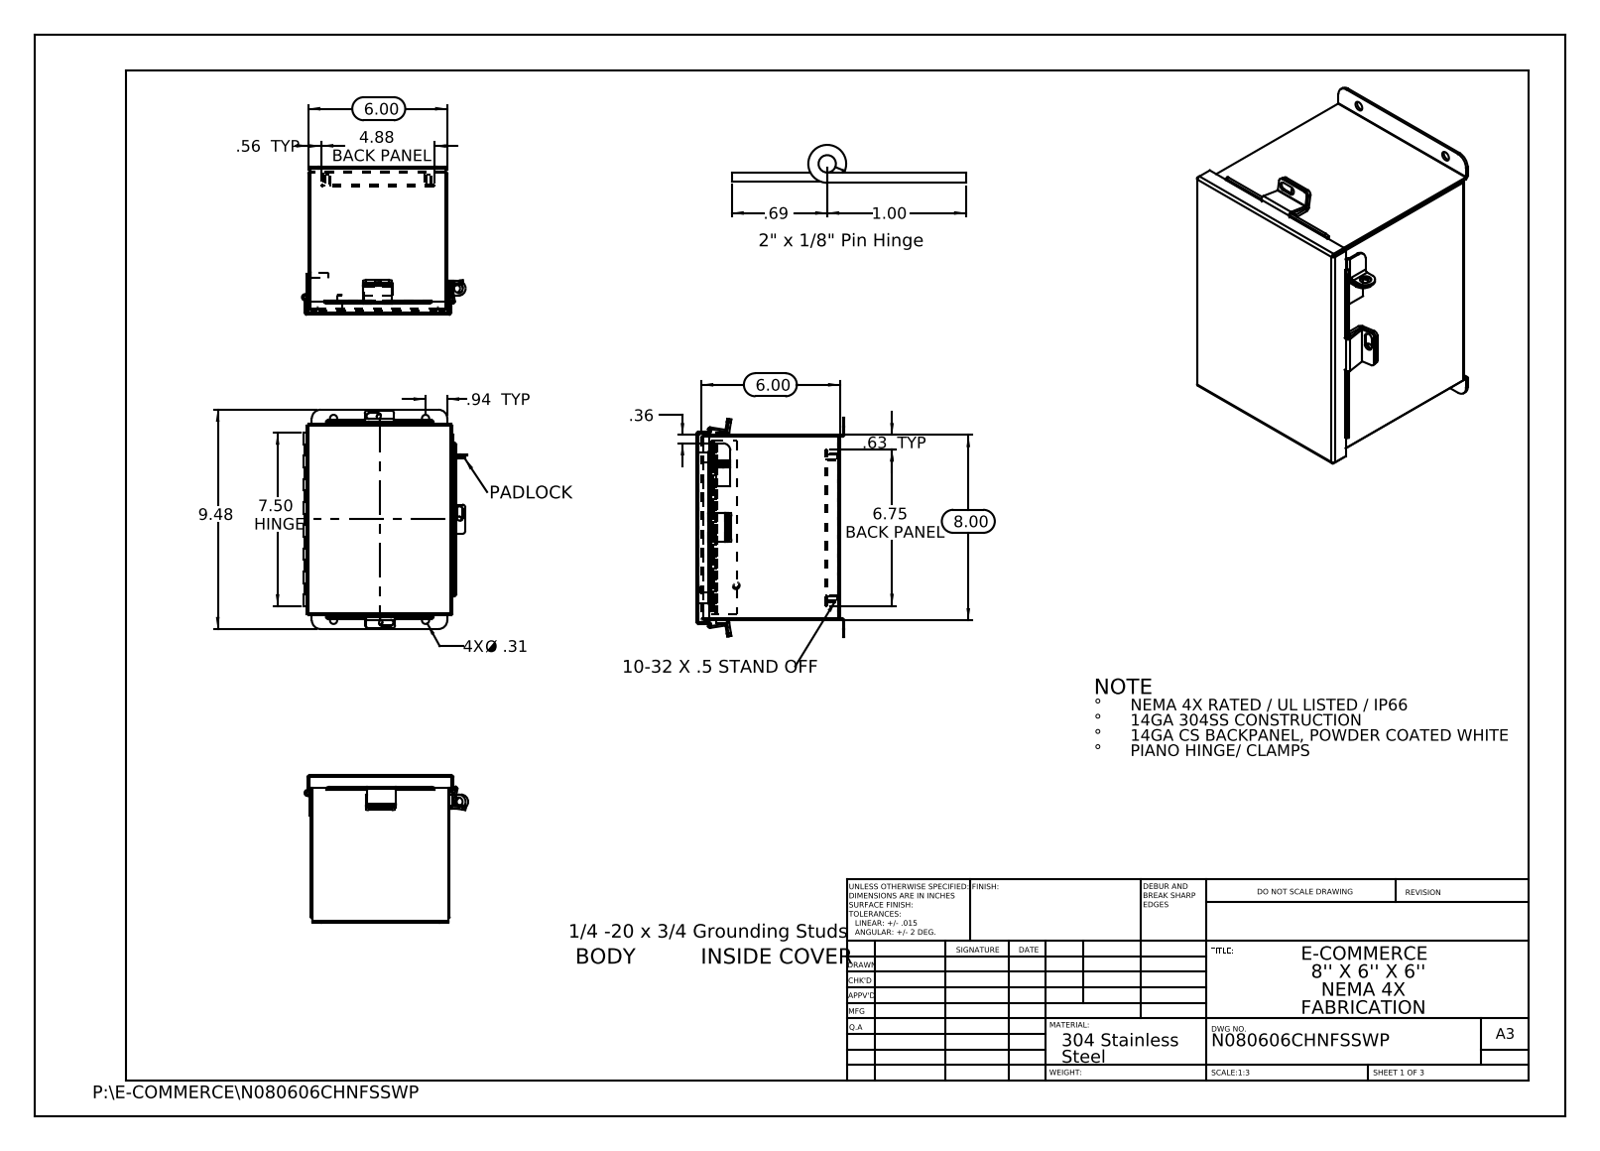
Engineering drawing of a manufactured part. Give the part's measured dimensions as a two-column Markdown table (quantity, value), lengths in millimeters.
| quantity | value |
| --- | --- |
| part name | N080606CHNFSSWP JIC Clamp Bracket; N080606CHNFSSWP JIC_Cover_Template; N080606CHNFSSWP JIC_Standoff; N080606CHNFSSWP _JIC Hinge (+8 more) |
| STEP written by | SolidWorks 2013 (CONFIG_CONTROL_DESIGN) |
| units | millimeters |
| bodies | 21 solids, 584 faces (363 planar, 201 cylindrical, 20 other) |
| overall size | 240.7 × 179.6 × 162.3 |
| volume | 437 400 mm³ |
| surface area | 474 000 mm² |
| round holes (diameter × count) | 6.4 × 7, 4.7 × 4, 7.9 × 4, 3.2 × 1, 3.2 × 1, 9.5 × 1, 9.5 × 1 |
| round bosses / shafts (diameter × count) | 8 × 4, 8 × 2, 6 × 2, 6.9 × 1, 6.4 × 1 |
| partial cylindrical surfaces (radius × count) | 0.3 × 13, 0.2 × 12, 2.2 × 12, 3.2 × 10, 2.1 × 6, 2.5 × 6, 3.4 × 6, 9.5 × 4 |
| main face-to-face distances | 1.9, 150.5, 155.7, 201.3, 152.4, 148.6, 153.7, 157.6, 199.4, 203.2 |
| hole center spacings | 33.4, 111.1, 188.7, 216.4, 101, 111.1, 155.6, 191.2 |
